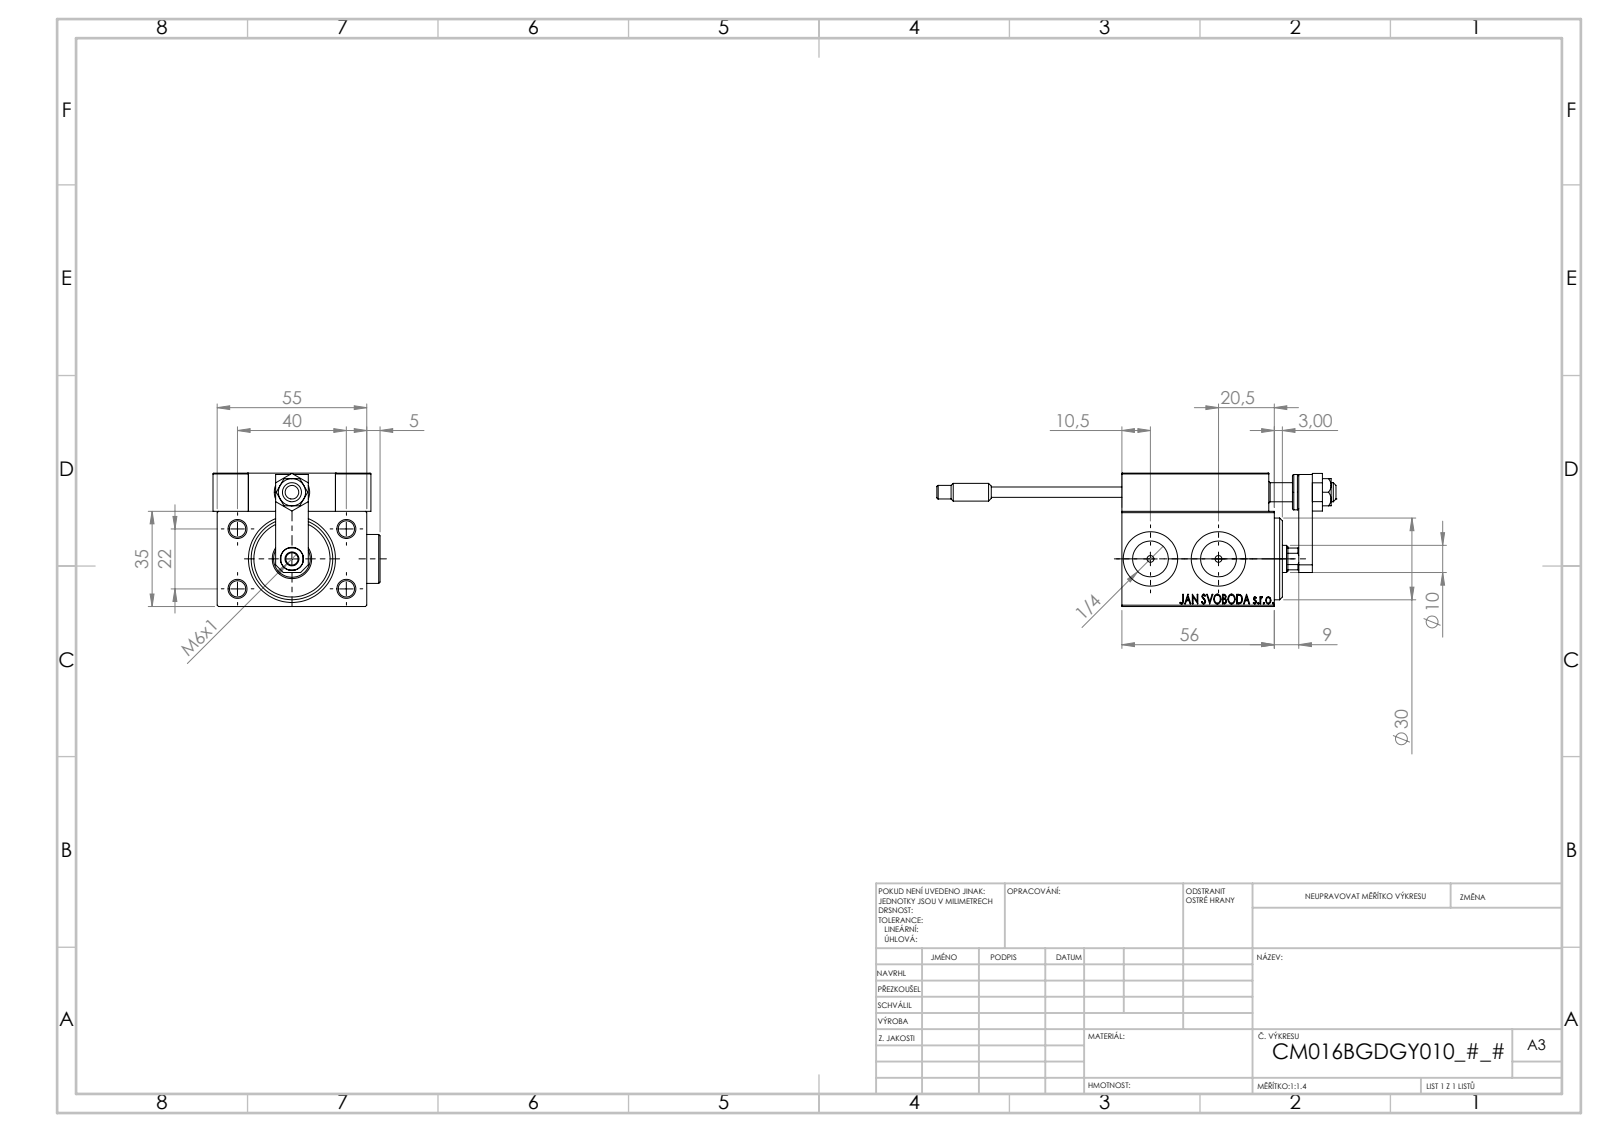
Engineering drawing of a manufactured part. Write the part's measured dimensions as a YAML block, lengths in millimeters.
part_name: "SWITCH DIM B,W; TYC_L79; V450CM_B_VCP; V450CM_B_Body (+7 more)"
step_written_by: "SolidWorks 2019 (CONFIG_CONTROL_DESIGN)"
units: millimeters
bodies: {solids: 26, faces: 1394, planar: 597, cylindrical: 208, other: 589}
overall_size: [146.7, 61.4, 49]
volume: 143940
surface_area: 50262
round_holes:
  - {diameter: 8, count: 5}
  - {diameter: 3.2, count: 4}
  - {diameter: 4, count: 4}
  - {diameter: 6, count: 4}
  - {diameter: 2.5, count: 2}
  - {diameter: 5, count: 2}
  - {diameter: 13.16, count: 2}
  - {diameter: 20, count: 2}
  - {diameter: 4.5, count: 1}
  - {diameter: 7, count: 1}
  - {diameter: 8.5, count: 1}
  - {diameter: 10, count: 1}
round_bosses_or_shafts:
  - {diameter: 5, count: 4}
  - {diameter: 18, count: 2}
  - {diameter: 6.5, count: 2}
  - {diameter: 3.8, count: 2}
  - {diameter: 13, count: 1}
  - {diameter: 11, count: 1}
partial_cylinders:
  - {radius: 0.3, count: 26}
  - {radius: 3, count: 2}
  - {radius: 4.5, count: 1}
face_to_face_distances: [35, 14, 49, 5, 3, 10, 1.5, 7, 55, 13]
hole_center_spacings: [22.83, 8.25, 11.37, 20, 22, 23.41, 24.13, 29.59]
